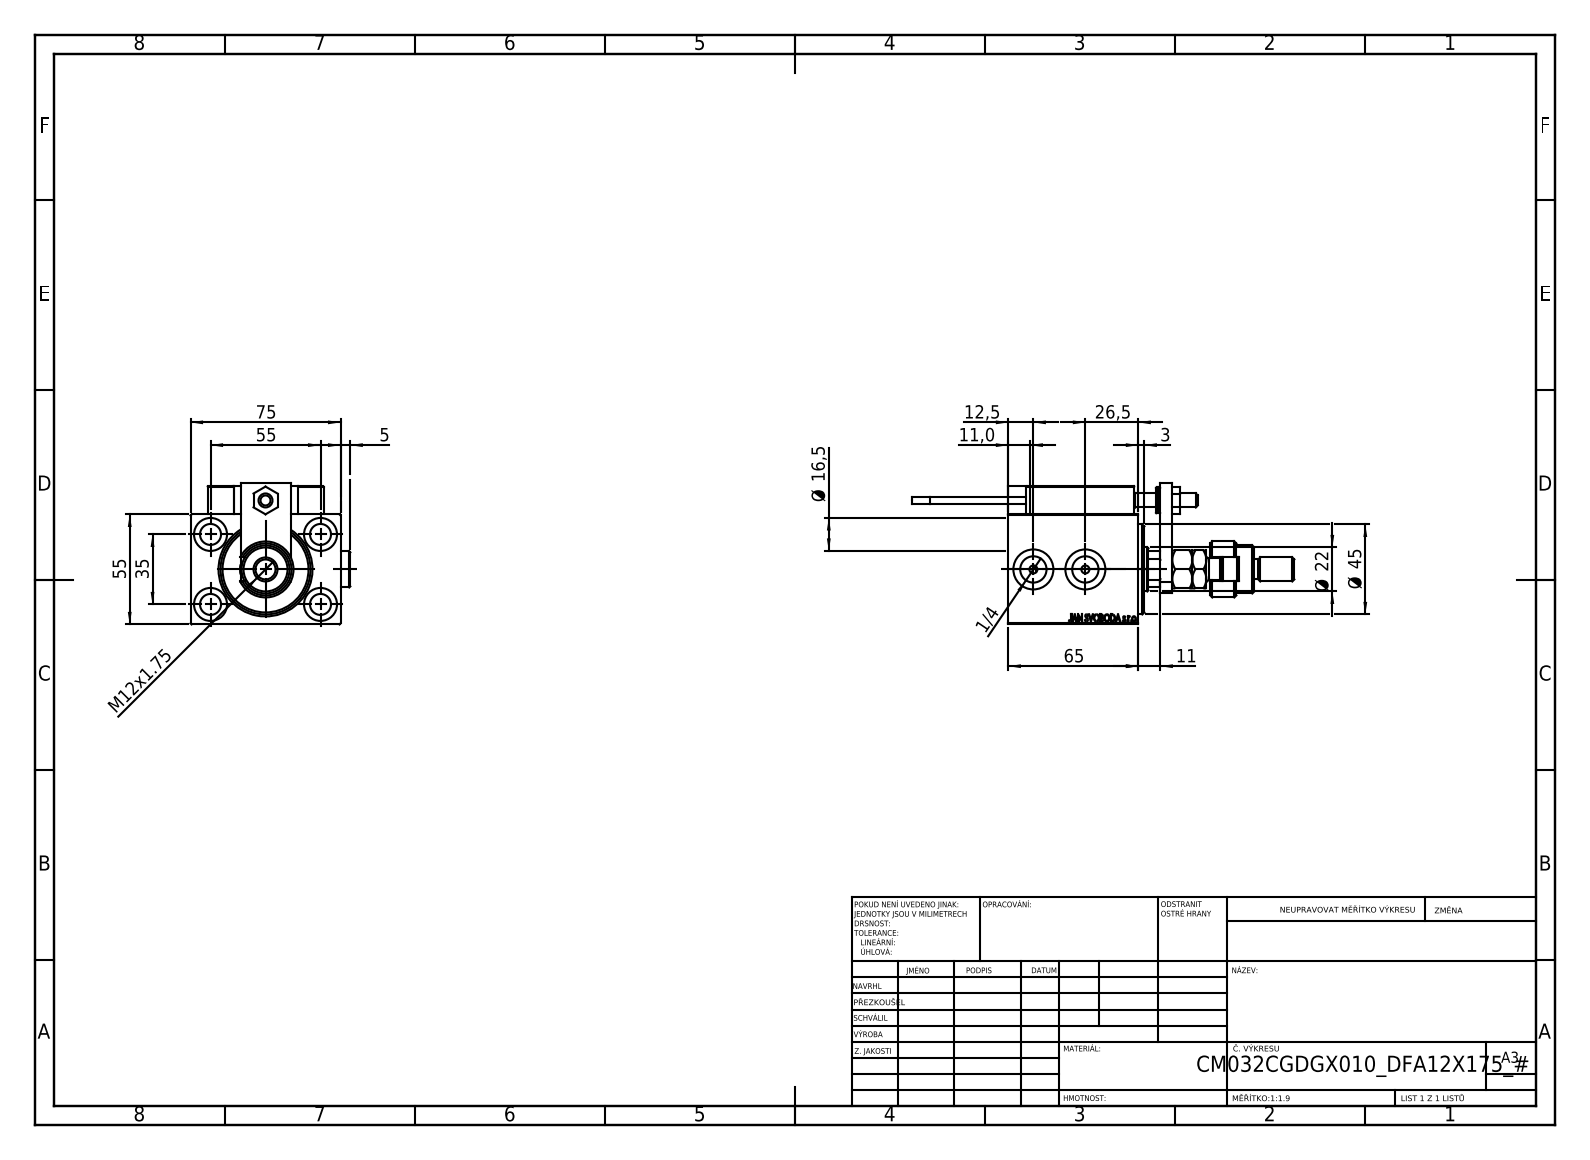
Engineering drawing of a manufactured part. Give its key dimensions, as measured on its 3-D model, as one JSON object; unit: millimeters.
{"part_name": "Zatka_OIL_PORT; ALLEN BOLT D8; ALLEN BOLT D5; ZARAZKA (+7 more)", "step_written_by": "SolidWorks 2019 (CONFIG_CONTROL_DESIGN)", "units": "millimeters", "bodies": {"solids": 27, "faces": 1420, "planar": 623, "cylindrical": 215, "other": 582}, "overall_size": [191, 79.9, 70.5], "volume_mm3": 294781, "surface_area_mm2": 89508, "round_holes": [[4, 6], [8, 5], [10.5, 5], [16.5, 5], [3.2, 4], [5, 2], [13.16, 2], [20, 2], [7, 1], [22, 1], [25.5, 1], [32, 1]], "round_bosses_or_shafts": [[18, 3], [11, 2], [5, 2], [3.8, 2], [28, 1], [24, 1], [13, 1], [12, 1]], "partial_cylinders_radius": [[0.3, 30], [3, 2], [9.75, 1], [10.5, 1]], "face_to_face_distances": [55, 14, 75, 11, 3, 54, 5, 69, 22, 68], "hole_center_spacings": [32.6, 11.37, 17.12, 20, 27.8, 29.59, 29.69, 32.32]}
